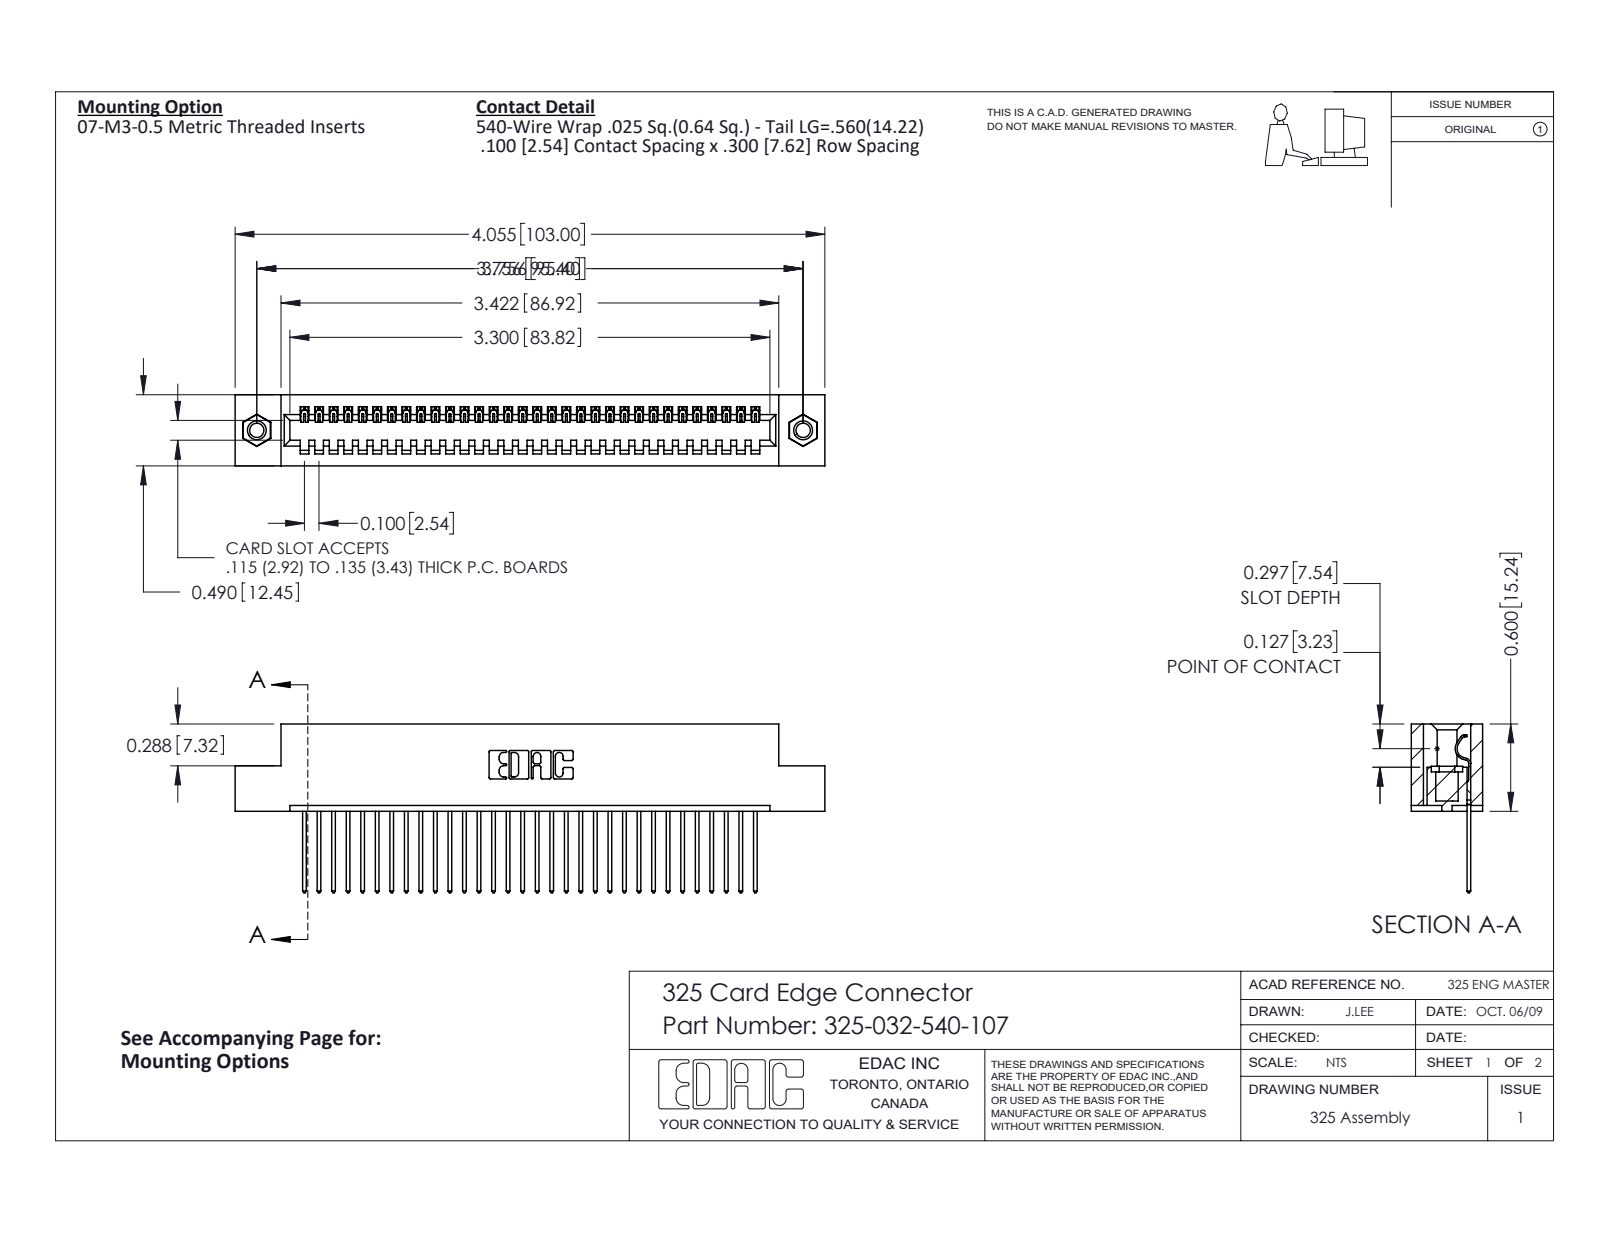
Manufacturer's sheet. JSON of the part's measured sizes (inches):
{"part_name": "325-032-540-107; 345-250-001_345-250-005-103; 325-292-001_325-293-140; 325 Part_TI", "step_written_by": "SolidWorks 2016 (CONFIG_CONTROL_DESIGN)", "units": "inches", "bodies": {"solids": 35, "faces": 2030, "planar": 1446, "cylindrical": 568, "other": 16}, "overall_size": [4.055, 1.16, 0.49], "volume_in3": 0.795, "surface_area_in2": 22.34, "round_holes": [[0.098, 2], [0.125, 2], [0.16, 2]], "round_bosses_or_shafts": [[0.155, 2]], "partial_cylinders_radius": [[0.006, 64], [0.01, 64], [0.01, 22], [0.007, 6], [0.031, 6], [0.026, 3], [0.014, 1], [0.022, 1]], "face_to_face_distances": [0.083, 0.407, 0.3, 0.49, 0.107, 0.383, 0.025, 0.325, 0.04, 0.1], "hole_center_spacings": [3.756]}
